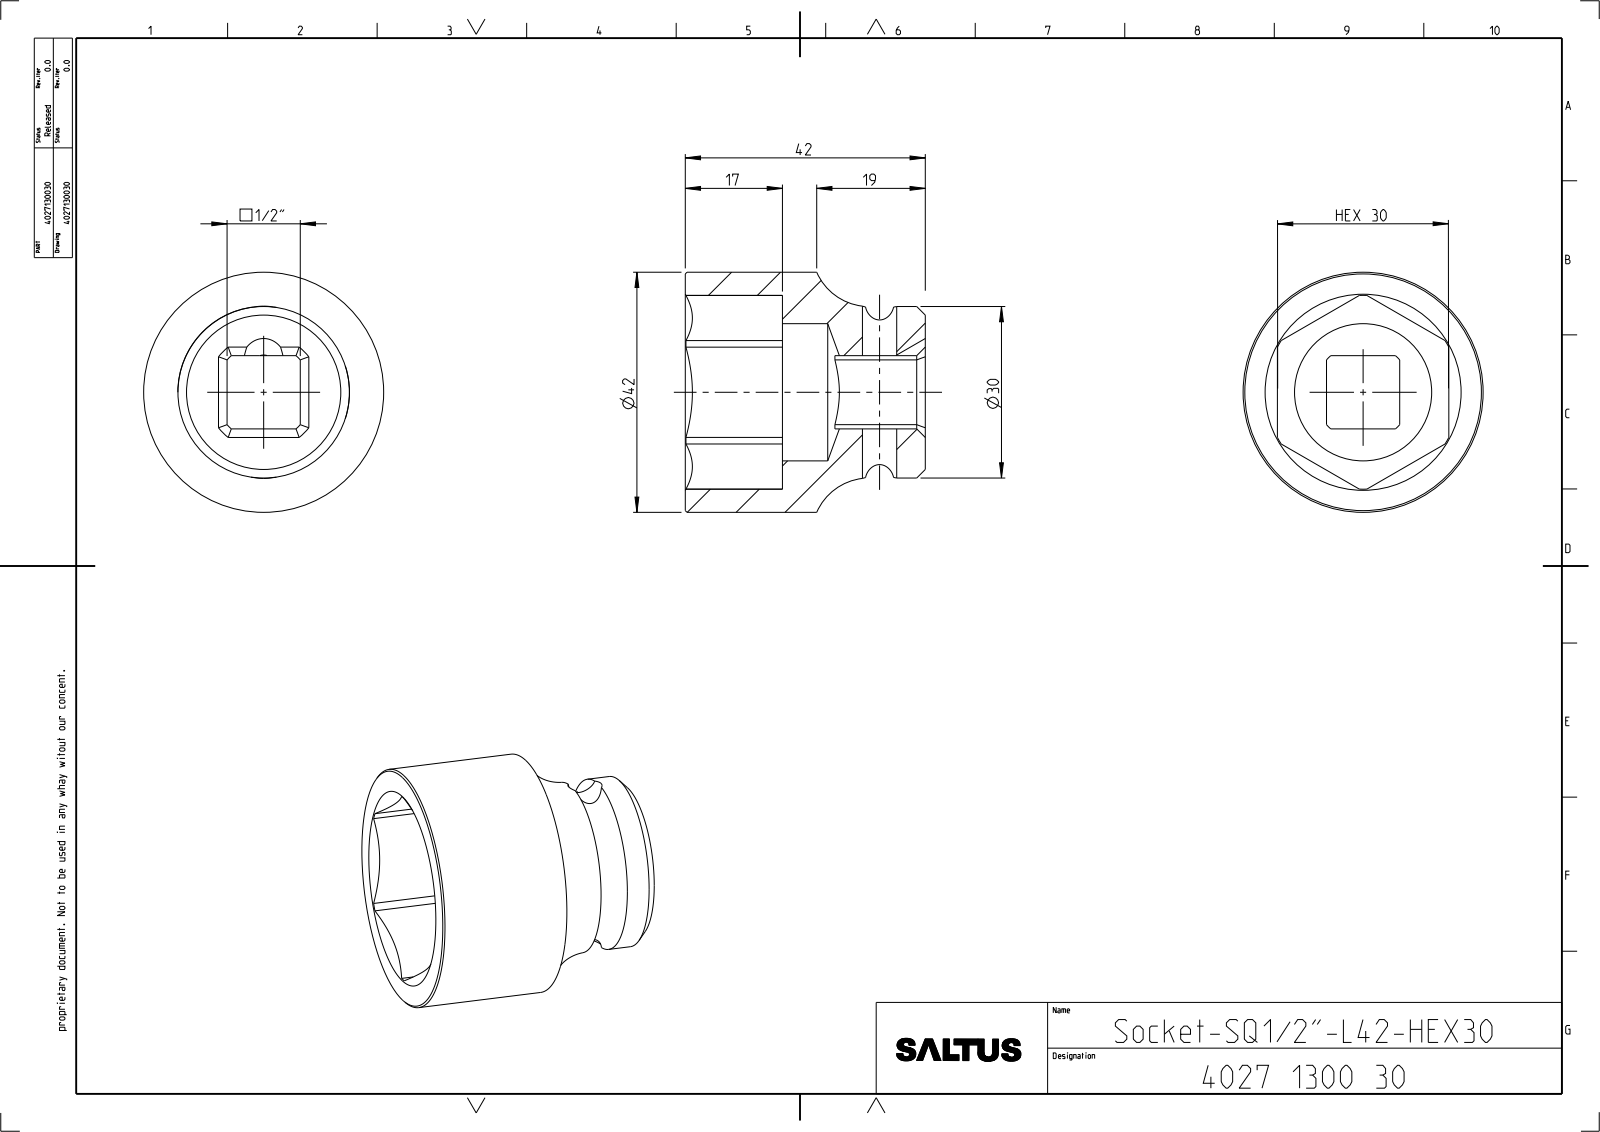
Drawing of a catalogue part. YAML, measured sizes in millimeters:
part_name: "4027130030"
step_written_by: "CREO PARAMETRIC BY PTC INC, 2022414 (CONFIG_CONTROL_DESIGN)"
units: millimeters
bodies: {solids: 1, faces: 55, planar: 18, cylindrical: 21, other: 16}
overall_size: [42, 42, 42]
volume: 25750
surface_area: 10169
round_holes:
  - {diameter: 6, count: 1}
  - {diameter: 24, count: 1}
round_bosses_or_shafts:
  - {diameter: 42, count: 1}
  - {diameter: 30, count: 1}
partial_cylinders:
  - {radius: 4, count: 1}
  - {radius: 8.55, count: 1}
  - {radius: 16.95, count: 1}
face_to_face_distances: [30, 17, 25, 42, 8.59, 21.41, 12.82]
